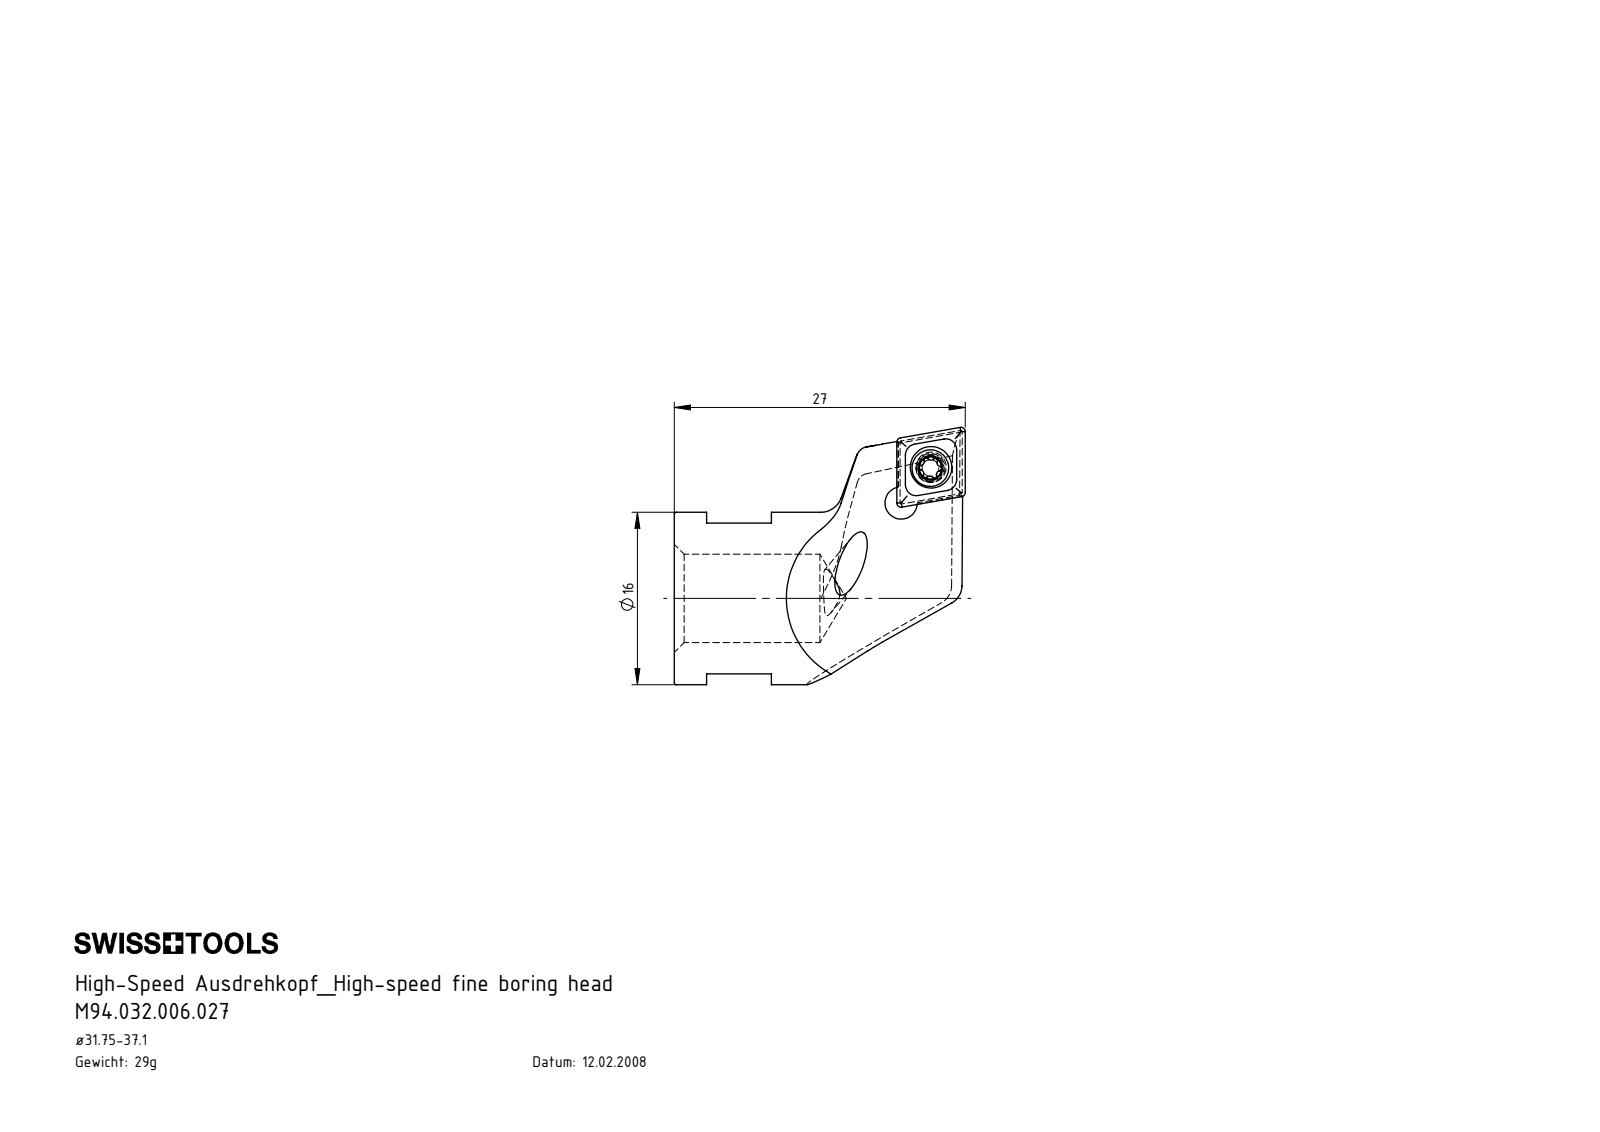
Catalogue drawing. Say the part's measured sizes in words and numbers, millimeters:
The part is named "CCMT060204; HS0.A32.K11.027; HS0-A32.K11.027_B; WCA-ER2.001.006_A". Its 3-D file was written by "SolidWorks 2017 (AUTOMOTIVE_DESIGN)". It is 3 solids with 97 faces: 34 planar, 23 cylindrical and 40 other. Overall it measures 27 by 23.88 by 16 millimeters. Its volume is 3 584 cubic millimeters and its surface area 2 272 square millimeters. Round holes: 1 of diameter 2.05, 1 of diameter 2.8, 1 of diameter 3, 1 of diameter 3.85, 1 of diameter 8.2. Round bosses or shafts: 1 of diameter 16, 1 of diameter 3.4, 1 of diameter 2.5. Partial cylindrical surfaces (rounded edges, fillets, slot ends): 6 of radius 0.21, 5 of radius 0.36, 1 of radius 0.36, 1 of radius 1.5, 1 of radius 1.8, 1 of radius 2. The main face-to-face distances are 7.9, 5.62, 2.28, 14, 6, 8, 2.38, 9, 3, 20.8.
